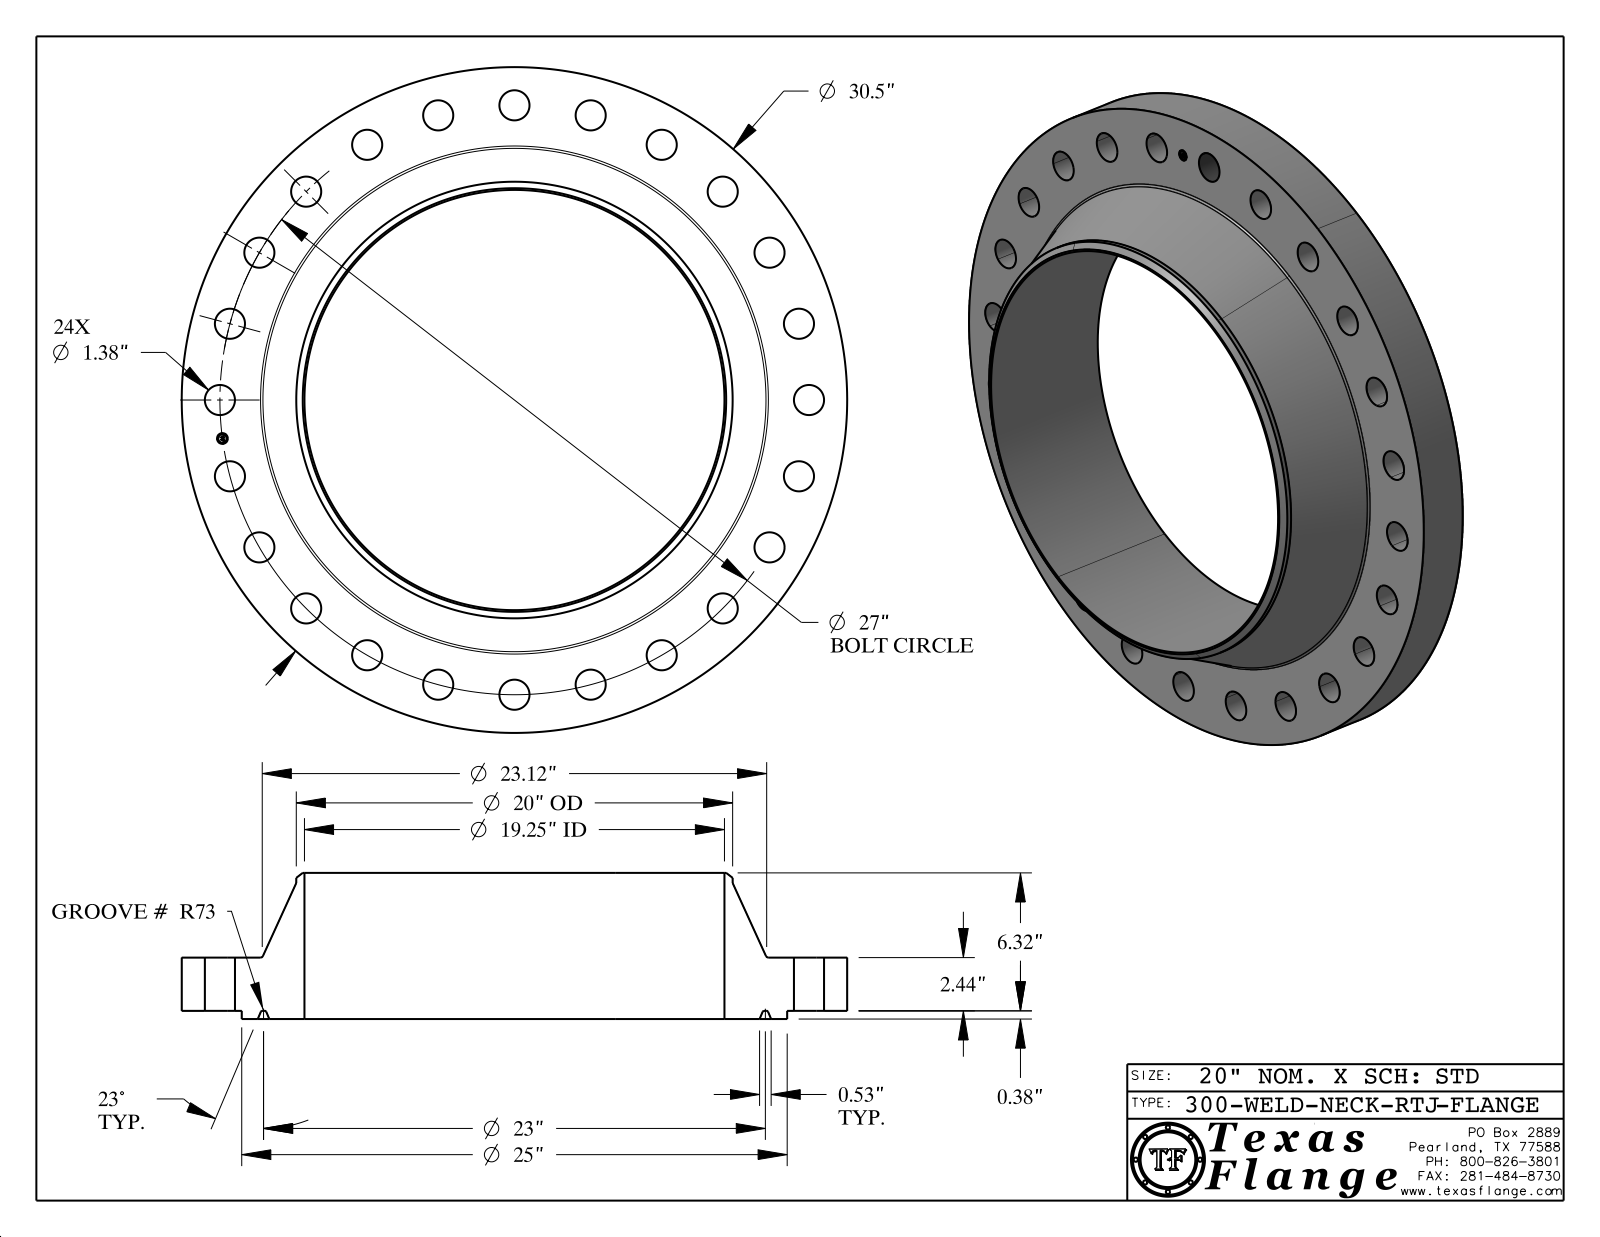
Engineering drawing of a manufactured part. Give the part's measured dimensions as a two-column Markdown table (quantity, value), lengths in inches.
| quantity | value |
| --- | --- |
| part name | 300-WELD-NECK-RTJ |
| STEP written by | CATIA V5 STEP AP214 (AUTOMOTIVE_DESIGN) |
| units | inches |
| bodies | 1 solid, 461 faces (371 planar, 76 cylindrical, 14 other) |
| overall size | 30.5 × 30.5 × 6.695 |
| volume | 1 314 in³ |
| surface area | 1 931 in² |
| round holes (diameter × count) | 1.38 × 24, 0.495 × 1, 19.25 × 1 |
| round bosses / shafts (diameter × count) | 0.03 × 8, 30.5 × 1, 25 × 1, 20 × 1, 0.39 × 1 |
| main face-to-face distances | 2.44, 0.375, 2.815, 6.695, 6.32, 3.88, 2.8, 2.425, 0.015, 3.895 |
| hole center spacings | 13.5, 3.524, 6.988, 10.333, 16.437, 24.945, 26.769, 21.421 |
